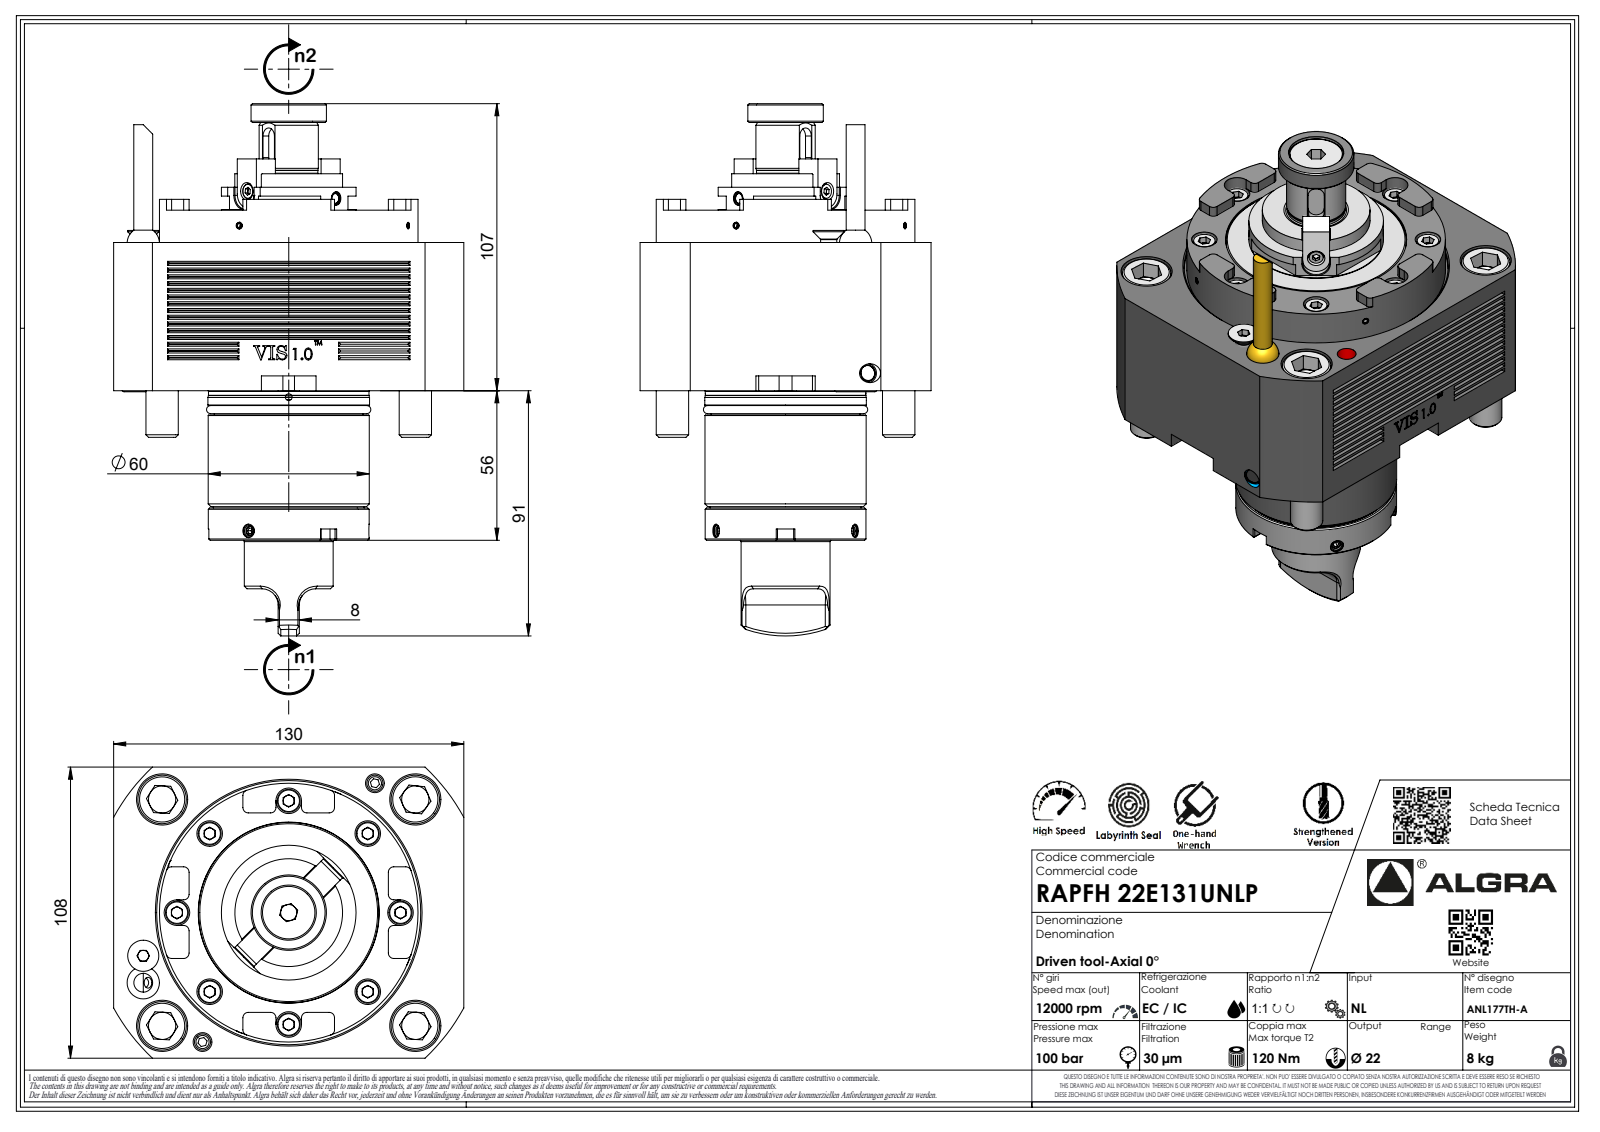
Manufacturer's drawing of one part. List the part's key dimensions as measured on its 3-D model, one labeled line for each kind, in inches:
Part name (STEP PRODUCT): RAPFH22E131UNLP
STEP written by: SolidWorks 2023 (AUTOMOTIVE_DESIGN)
Units: inches
Bodies: 1 solid, 533 faces (348 planar, 94 cylindrical, 91 other)
Overall size (bounding box): 7.776 × 5.118 × 4.252
Volume: 64.01 in³ · Surface area: 124.1 in²
Round holes (diameter × count): ⌀0.083 ×1, ⌀0.157 ×1
Round bosses / shafts (diameter × count): ⌀0.472 ×4, ⌀3.78 ×1, ⌀2.362 ×1, ⌀1.969 ×1, ⌀1.575 ×1, ⌀1.299 ×1, ⌀1.102 ×1, ⌀0.866 ×1
Partial cylindrical surfaces — rounded edges, fillets, slot ends (radius × count): R0.079 ×25, R0.315 ×8, R0.013 ×7, R0.02 ×7, R0.146 ×7, R0.236 ×6, R0.187 ×4, R0.197 ×3
Main face-to-face distances: 2.165, 4.252, 0.472, 2.638, 5.118, 2.185, 4.35, 4.823, 0.217, 2.421
